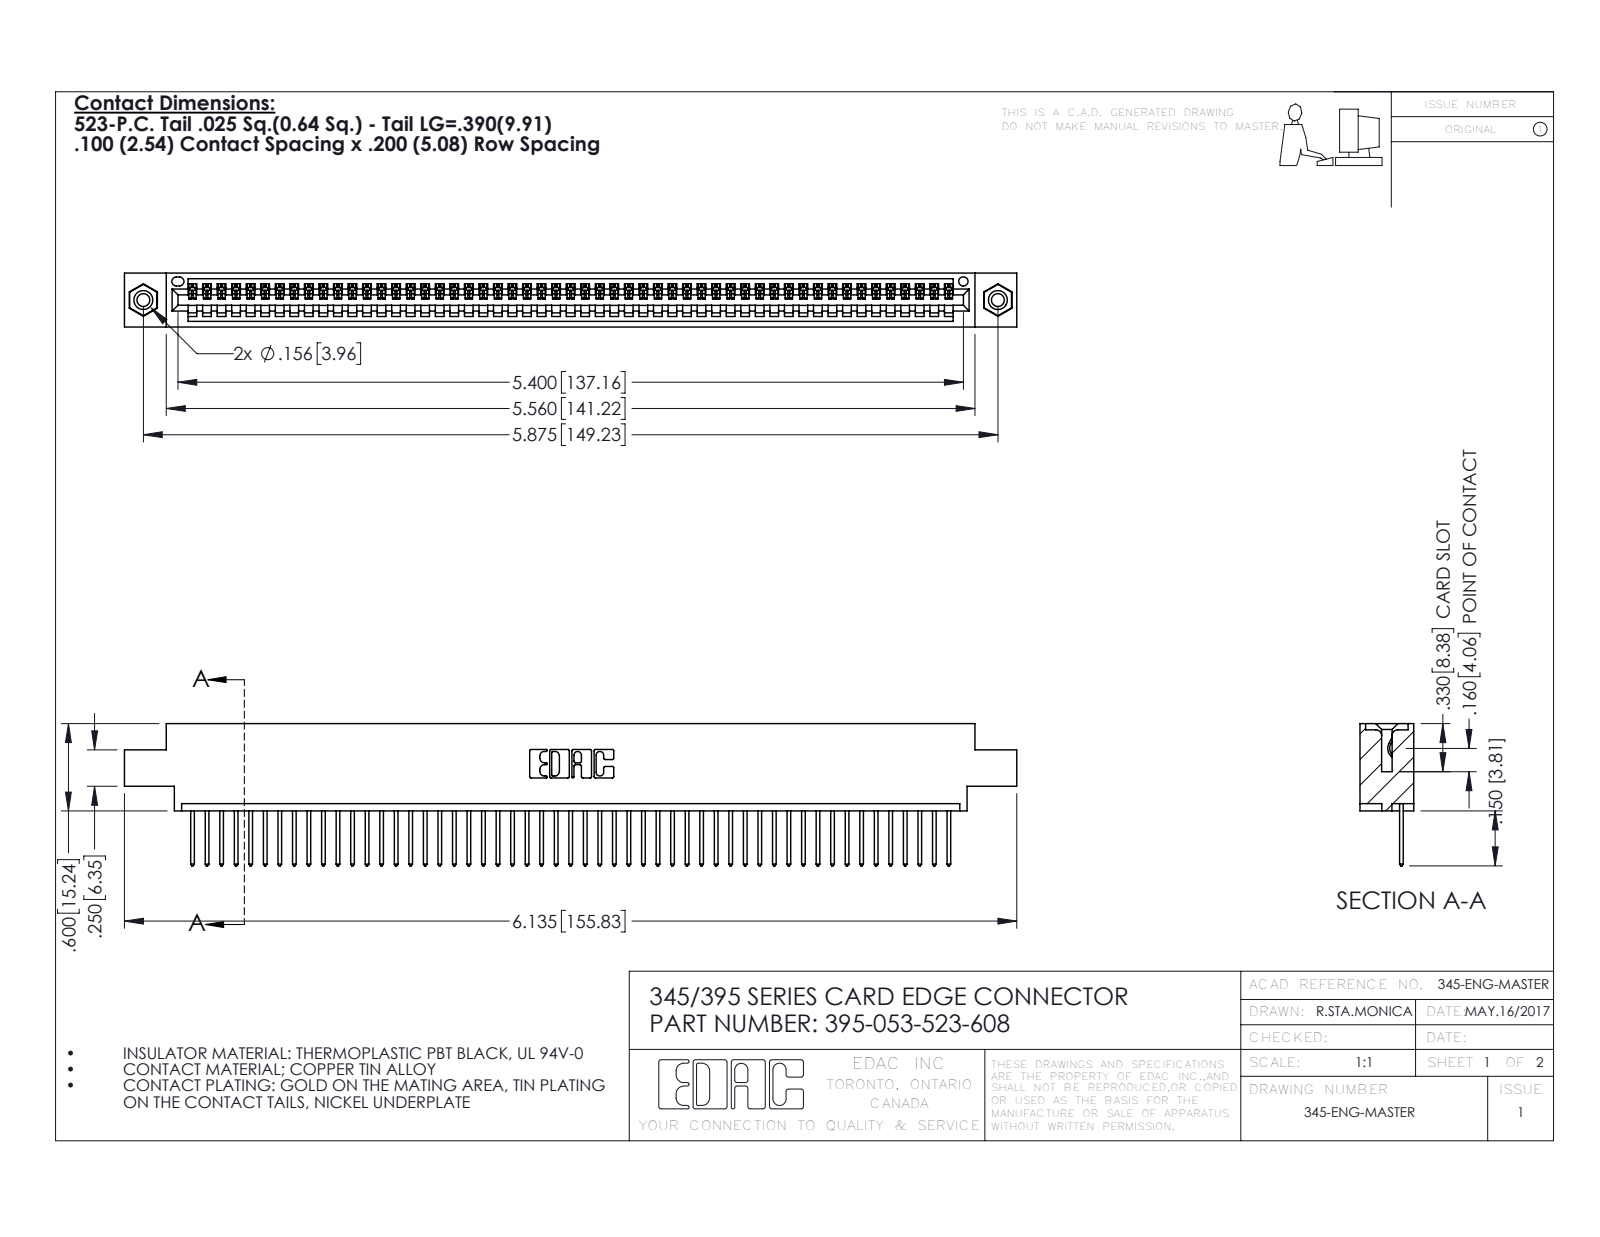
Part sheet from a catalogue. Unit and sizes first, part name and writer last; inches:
Units: inches
Overall size (bounding box): 6.135 × 0.977 × 0.37
Round holes (diameter × count): ⌀0.089 ×2, ⌀0.125 ×2, ⌀0.156 ×2, ⌀0.064 ×1
Round bosses / shafts (diameter × count): ⌀0.155 ×2
Partial cylindrical surfaces — rounded edges, fillets, slot ends (radius × count): R0.006 ×106, R0.01 ×106, R0.01 ×22, R0.007 ×6, R0.031 ×6, R0.026 ×3, R0.031 ×2, R0.04 ×2
Main face-to-face distances: 0.072, 0.298, 0.37, 0.098, 0.272, 0.025, 0.2, 0.225, 0.175, 0.149
Hole centre spacings: 0.27, 5.639, 5.875
Volume: 0.9 in³ · Surface area: 30.93 in²
Bodies: 56 solids, 3264 faces (2236 planar, 1012 cylindrical, 16 other)
Part name (STEP PRODUCT): 345-292-001_345-293-123; 345 Part_0.170 Offset - 0.156 Dia-TI; 395-053-523-608; 345-250-001_345-250-003-102
STEP written by: SolidWorks 2016 (CONFIG_CONTROL_DESIGN)
